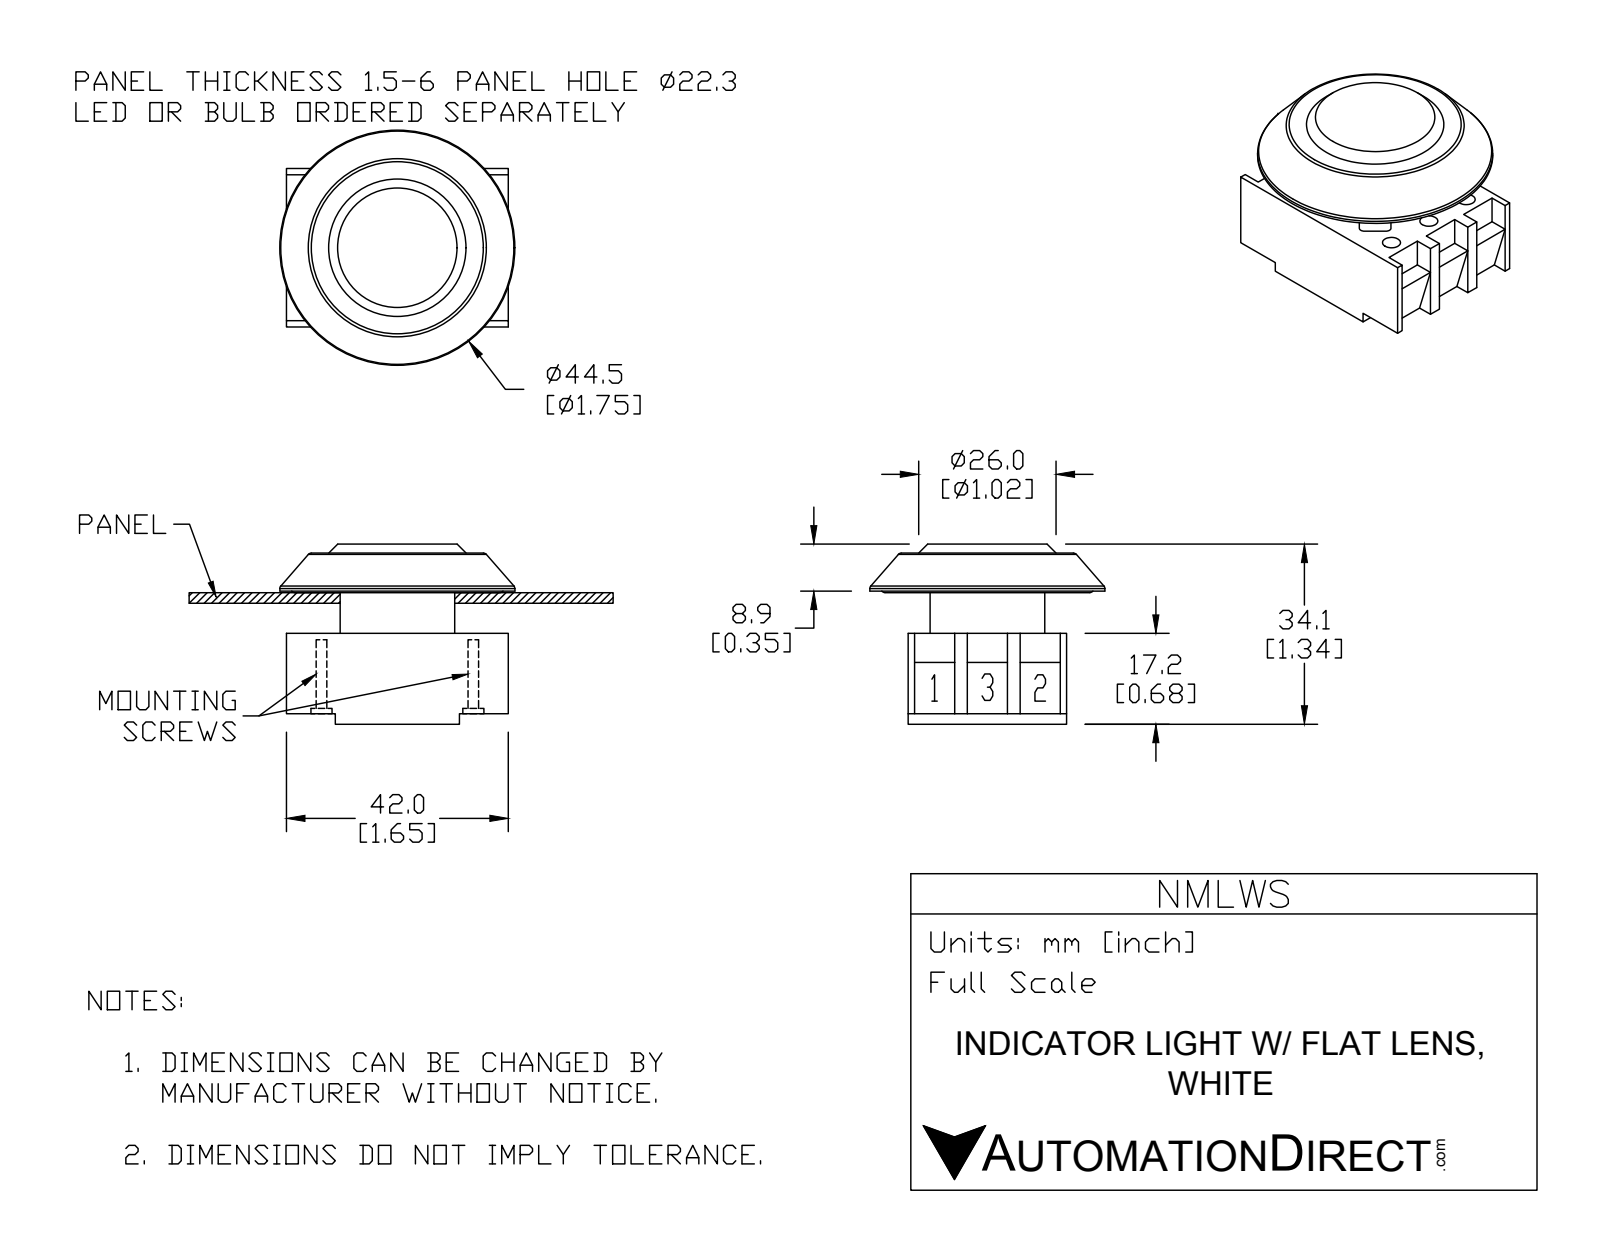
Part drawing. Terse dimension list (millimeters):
name: NMLWS
written by: SolidWorks 2015 (AUTOMOTIVE_DESIGN)
unit: mm
bodies: 6 solids, 209 faces (125 planar, 63 cylindrical, 21 other)
size: 44.5 × 44.5 × 34.1
volume: 23 947 mm³; area: 15 137 mm²
holes: 6× ⌀3.4, 6× ⌀5, 1× ⌀12.5
bosses: 2× ⌀4.6, 2× ⌀4, 1× ⌀44.5, 1× ⌀21.7
rounds: 8× R1, 5× R8.7, 1× R11
face distances: 30, 15.2, 8, 7.7, 9.2, 16.9, 8.9, 22.9, 10, 7.5
hole spacings: 10, 17.52, 30.45, 28.76, 14.38, 20, 35.03
